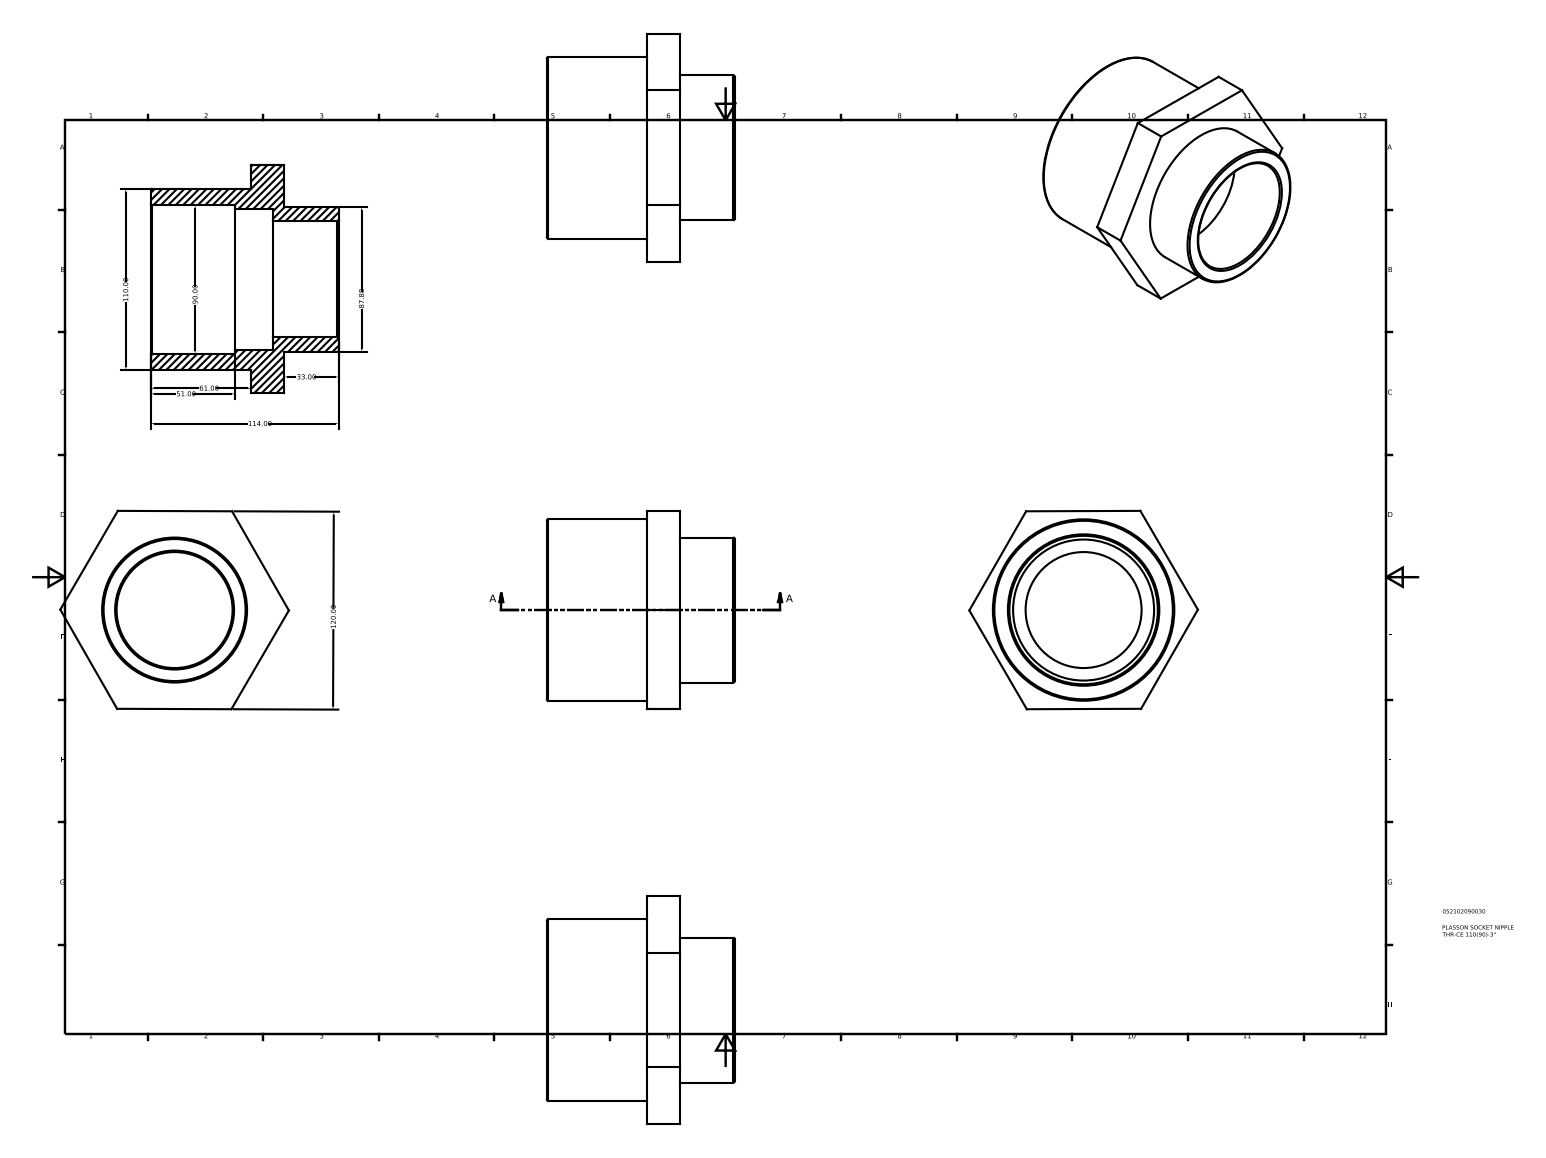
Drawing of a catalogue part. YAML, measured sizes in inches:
part_name: "052102090030"
step_written_by: "Autodesk Inventor 2015 (AUTOMOTIVE_DESIGN)"
units: inches
bodies: {solids: 1, faces: 21, planar: 12, cylindrical: 5, other: 4}
overall_size: [5.455, 4.734, 4.488]
volume: 25.42
surface_area: 131.3
round_holes:
  - {diameter: 2.768, count: 1}
  - {diameter: 3.366, count: 1}
  - {diameter: 3.543, count: 1}
round_bosses_or_shafts:
  - {diameter: 4.331, count: 1}
  - {diameter: 3.46, count: 1}
face_to_face_distances: [0.787, 2.402, 3.189, 2.929, 0.528, 0.26, 4.488, 2.087, 1.559, 1.299]
